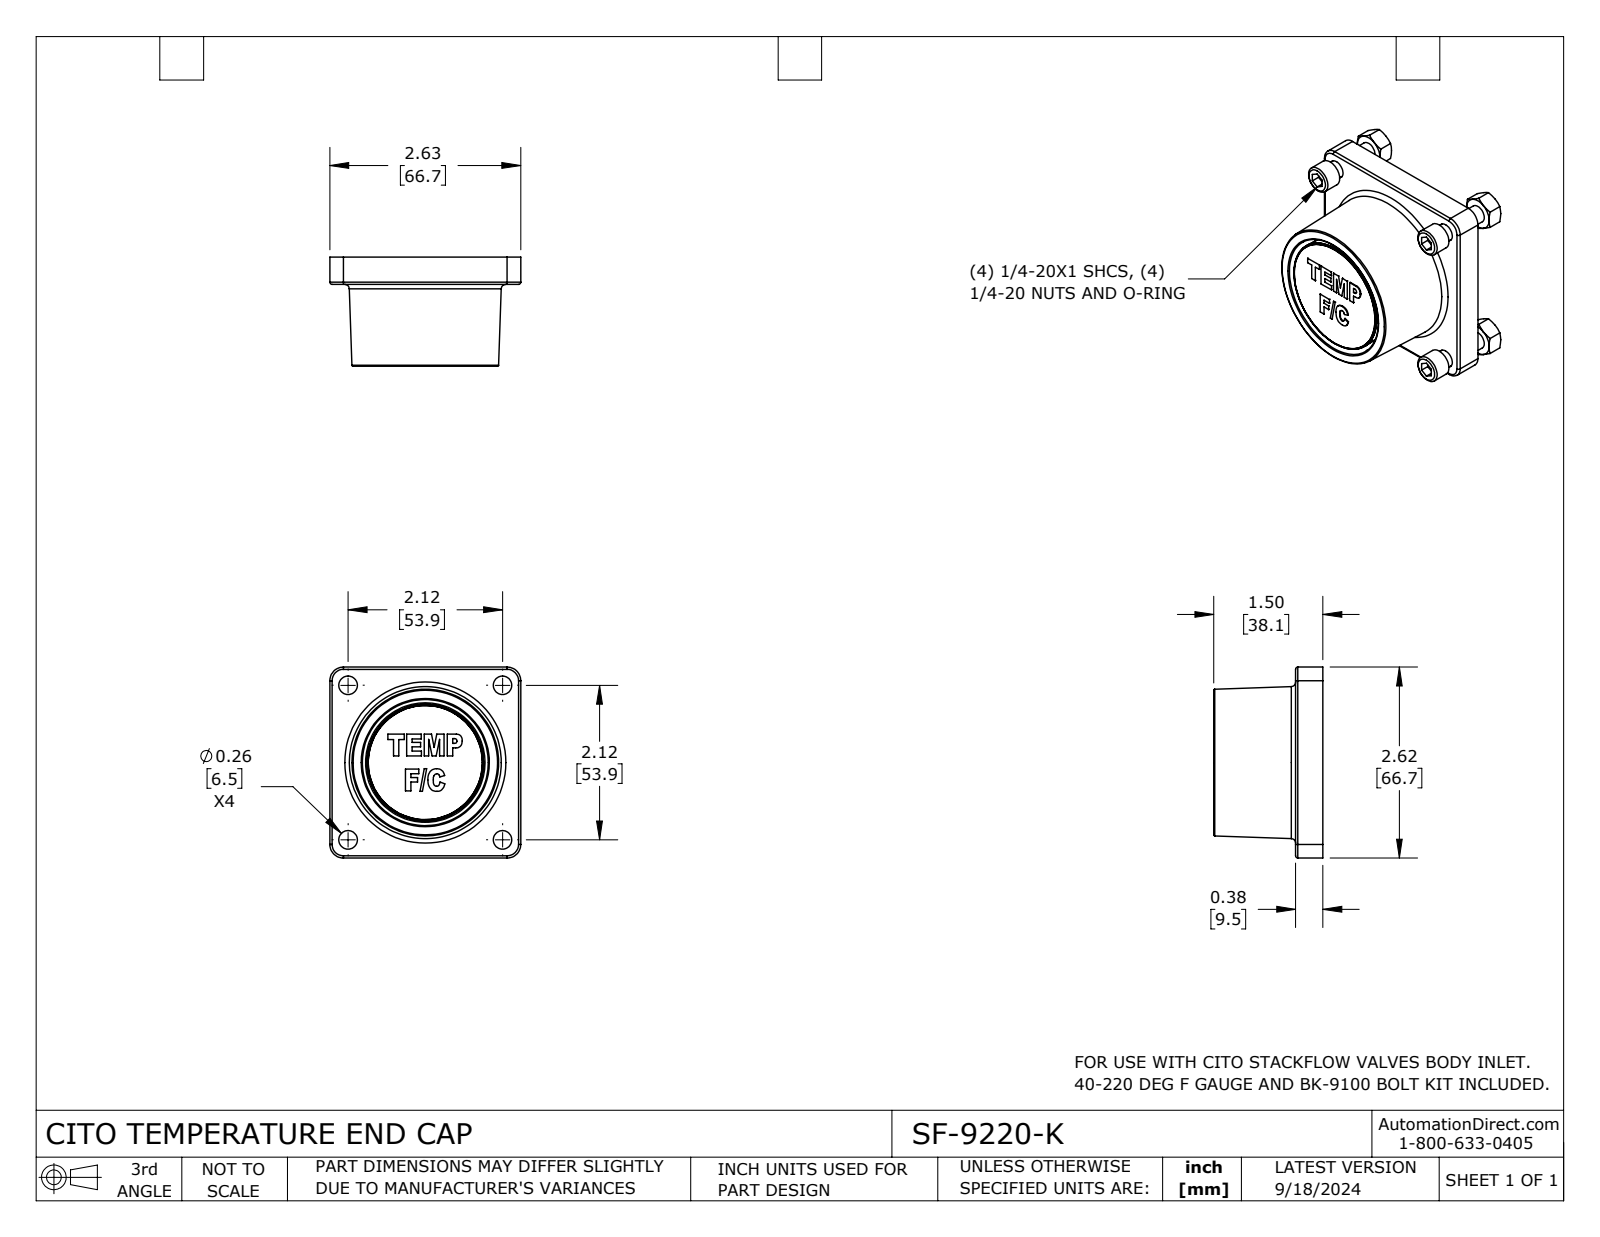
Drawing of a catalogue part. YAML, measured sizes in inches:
part_name: "SF-9220-K"
step_written_by: "SolidWorks 2023 (CONFIG_CONTROL_DESIGN)"
units: inches
bodies: {solids: 11, faces: 143, planar: 83, cylindrical: 18, other: 42}
overall_size: [2.625, 2.625, 1.5]
volume: 7.15
surface_area: 49.77
round_holes:
  - {diameter: 0.255, count: 4}
  - {diameter: 0.375, count: 1}
partial_cylinders:
  - {radius: 0.031, count: 4}
  - {radius: 0.187, count: 2}
  - {radius: 0.188, count: 2}
face_to_face_distances: [1.473, 0.473, 1, 0.375, 0.098, 1.098, 0.2, 0.175, 0.273, 1.273]
hole_center_spacings: [1.502, 2.124, 3.003]
